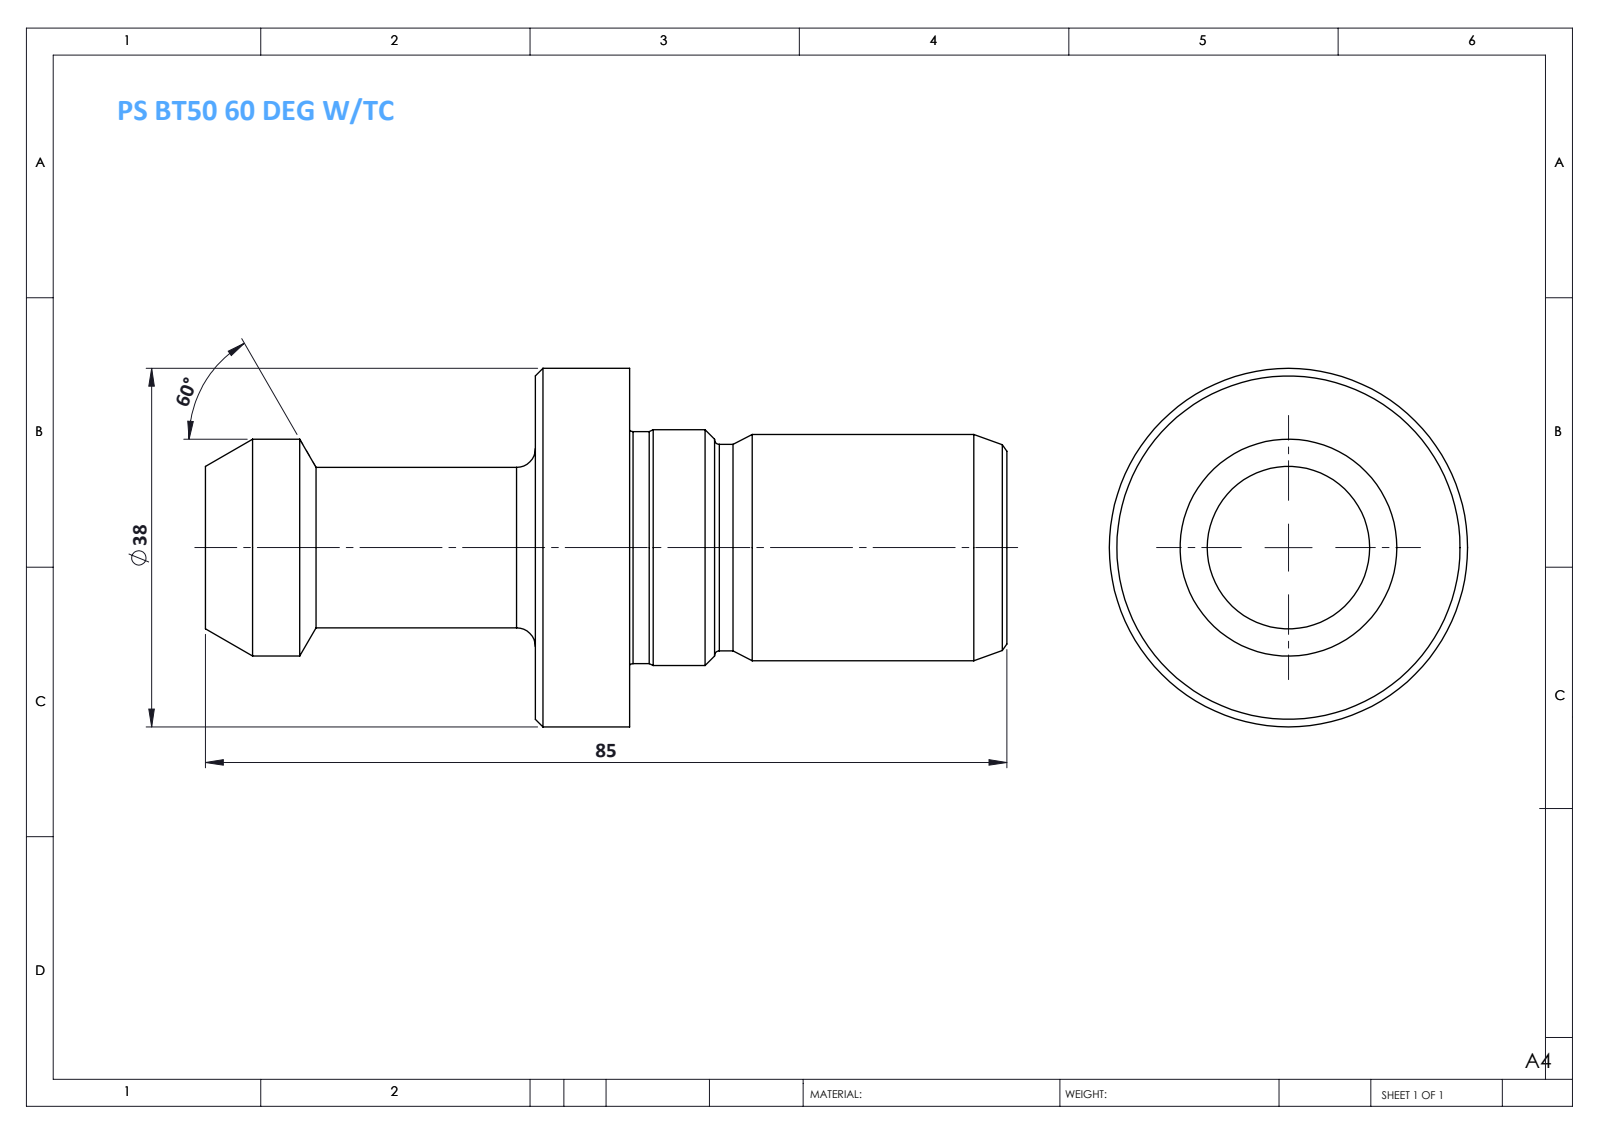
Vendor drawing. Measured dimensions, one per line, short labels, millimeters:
name: PS BT50 60 DEG W-TC
written by: SolidWorks 2014 (CONFIG_CONTROL_DESIGN)
unit: mm
bodies: 1 solid, 43 faces (5 planar, 14 cylindrical, 24 other)
size: 85 × 38 × 38
volume: 38 828 mm³; area: 8 522 mm²
bosses: 1× ⌀38, 1× ⌀25, 1× ⌀24.6, 1× ⌀24, 1× ⌀23, 1× ⌀21.9, 1× ⌀17
face distances: 10, 40, 50, 85, 45, 35, 31, 9, 19, 54
